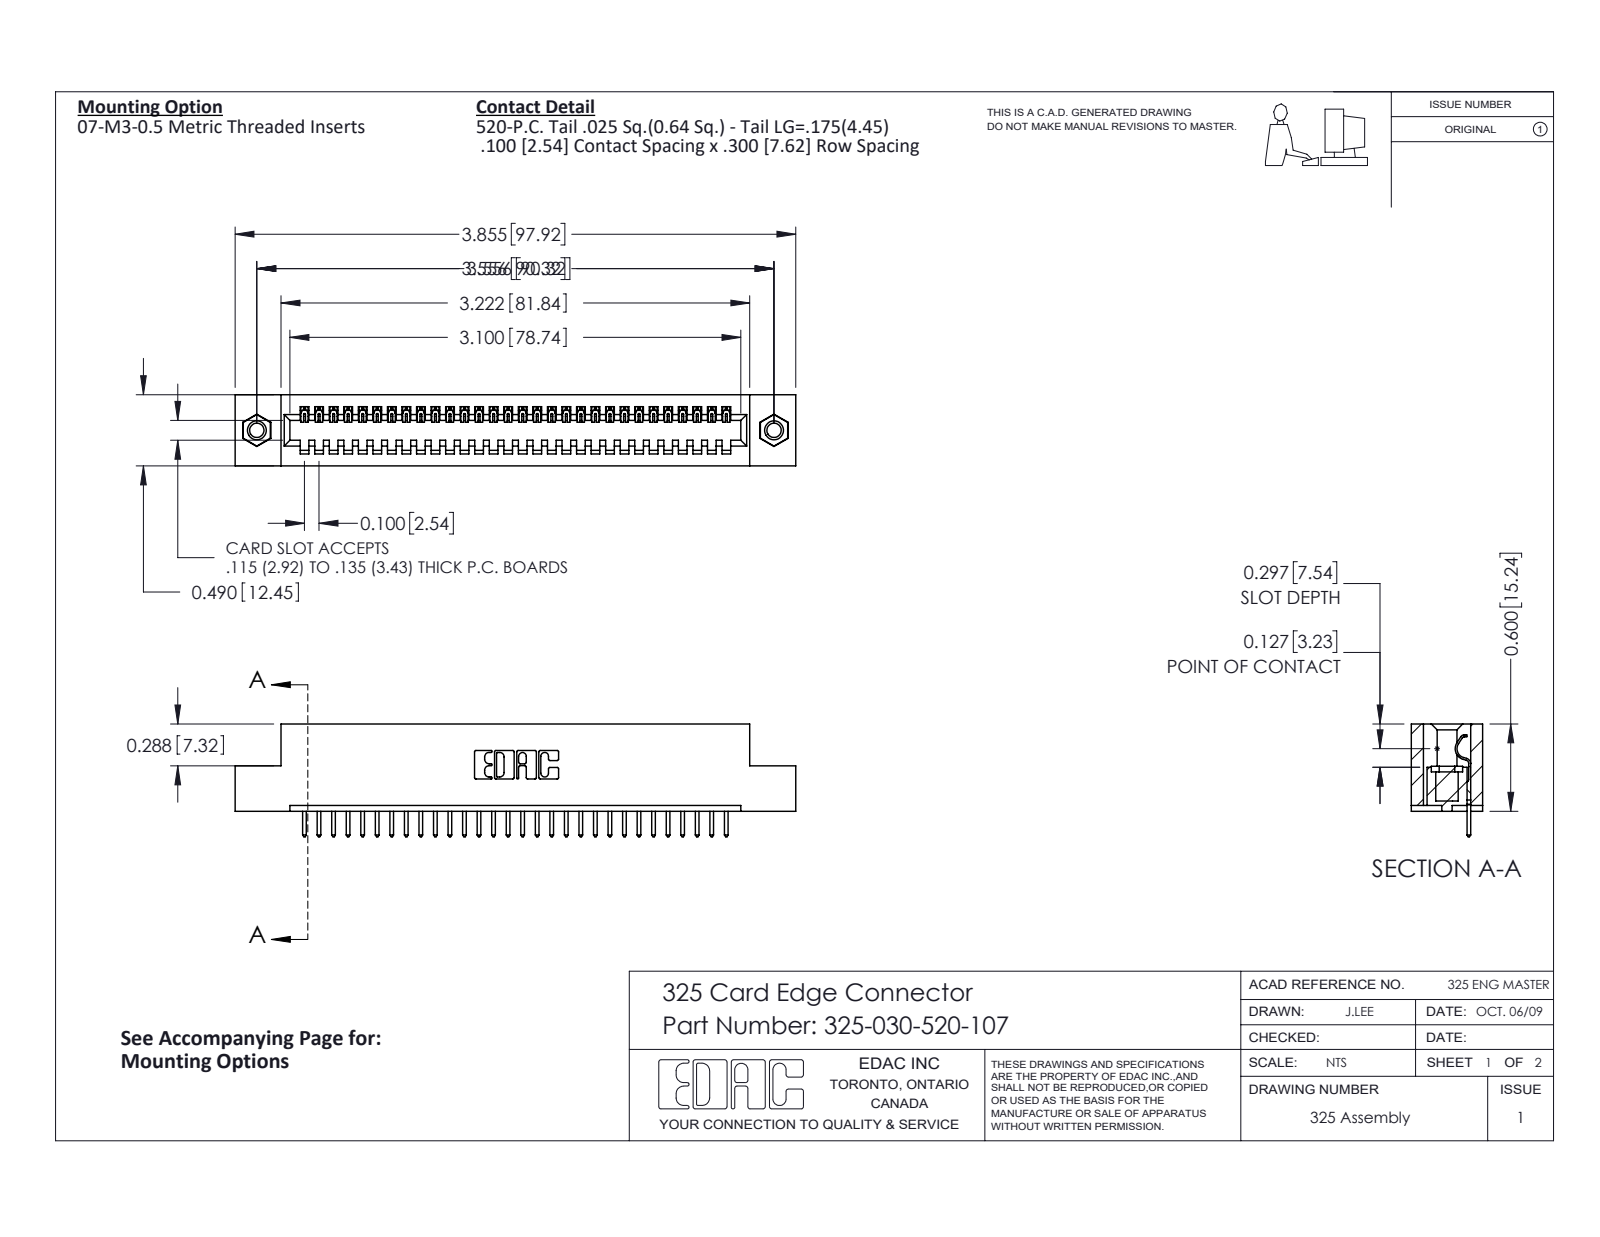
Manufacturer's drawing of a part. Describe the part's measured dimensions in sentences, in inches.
The part is named "325-292-001_325-293-120; 345-250-001_345-250-005-103; 325 Part_TI; 325-030-520-107". Its 3-D file was written by "SolidWorks 2016 (CONFIG_CONTROL_DESIGN)". It is 33 solids with 1914 faces: 1362 planar, 536 cylindrical and 16 other. Overall it measures 3.855 by 0.775 by 0.49 inches. Its volume is 0.747 cubic inches and its surface area 19.97 square inches. Round holes: 2 of diameter 0.098, 2 of diameter 0.125, 2 of diameter 0.16. Round bosses or shafts: 2 of diameter 0.155. Partial cylindrical surfaces (rounded edges, fillets, slot ends): 60 of radius 0.006, 60 of radius 0.01, 22 of radius 0.01, 6 of radius 0.007, 6 of radius 0.031, 3 of radius 0.026, 1 of radius 0.014, 1 of radius 0.022. The main face-to-face distances are 0.083, 0.407, 0.49, 0.3, 0.107, 0.383, 0.025, 0.325, 0.04, 0.56. The hole center spacings are 3.556.
